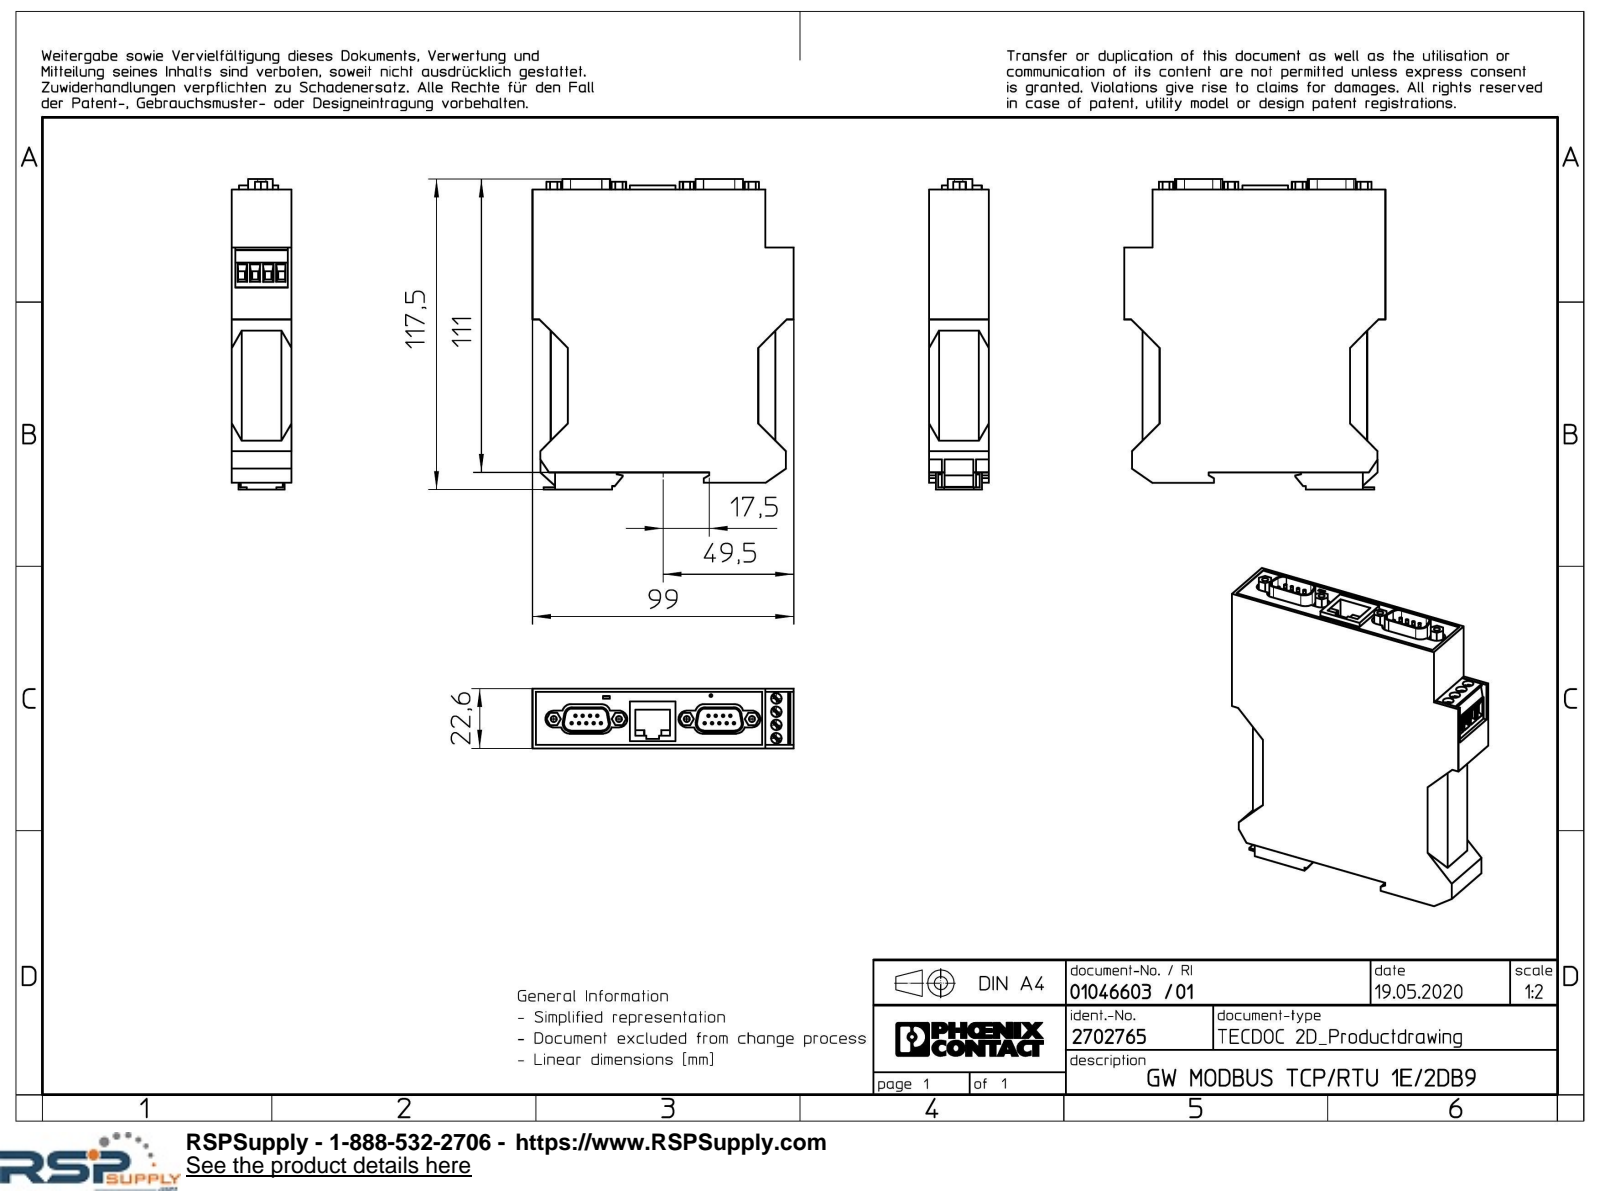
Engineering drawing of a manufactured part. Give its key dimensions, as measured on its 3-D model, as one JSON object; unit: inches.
{"part_name": "GW_MODBUS_TCP_RTU_1E_2DB9-select", "step_written_by": "Creo Elements/Direct Modeling 20.1A 29-Sep-2018 (C) Parametric Technology GmbH (AUTOMOTIVE_DESIGN)", "units": "inches", "bodies": {"solids": 1, "faces": 362, "planar": 280, "cylindrical": 82, "other": 0}, "overall_size": [4.626, 3.898, 0.89], "volume_in3": 13.32, "surface_area_in2": 50.88, "round_holes": [[0.09, 4], [0.157, 4], [0.043, 1]], "round_bosses_or_shafts": [[0.039, 18]], "partial_cylinders_radius": [[0.125, 12], [0.1, 8], [0.12, 8]], "face_to_face_distances": [0.89, 0.157, 3.624, 0.274, 4.205, 4.362, 3.35, 3.476, 3.203, 0.148], "hole_center_spacings": [0.197, 0.394, 0.974, 1.984, 0.373, 0.378, 0.462, 0.473]}
